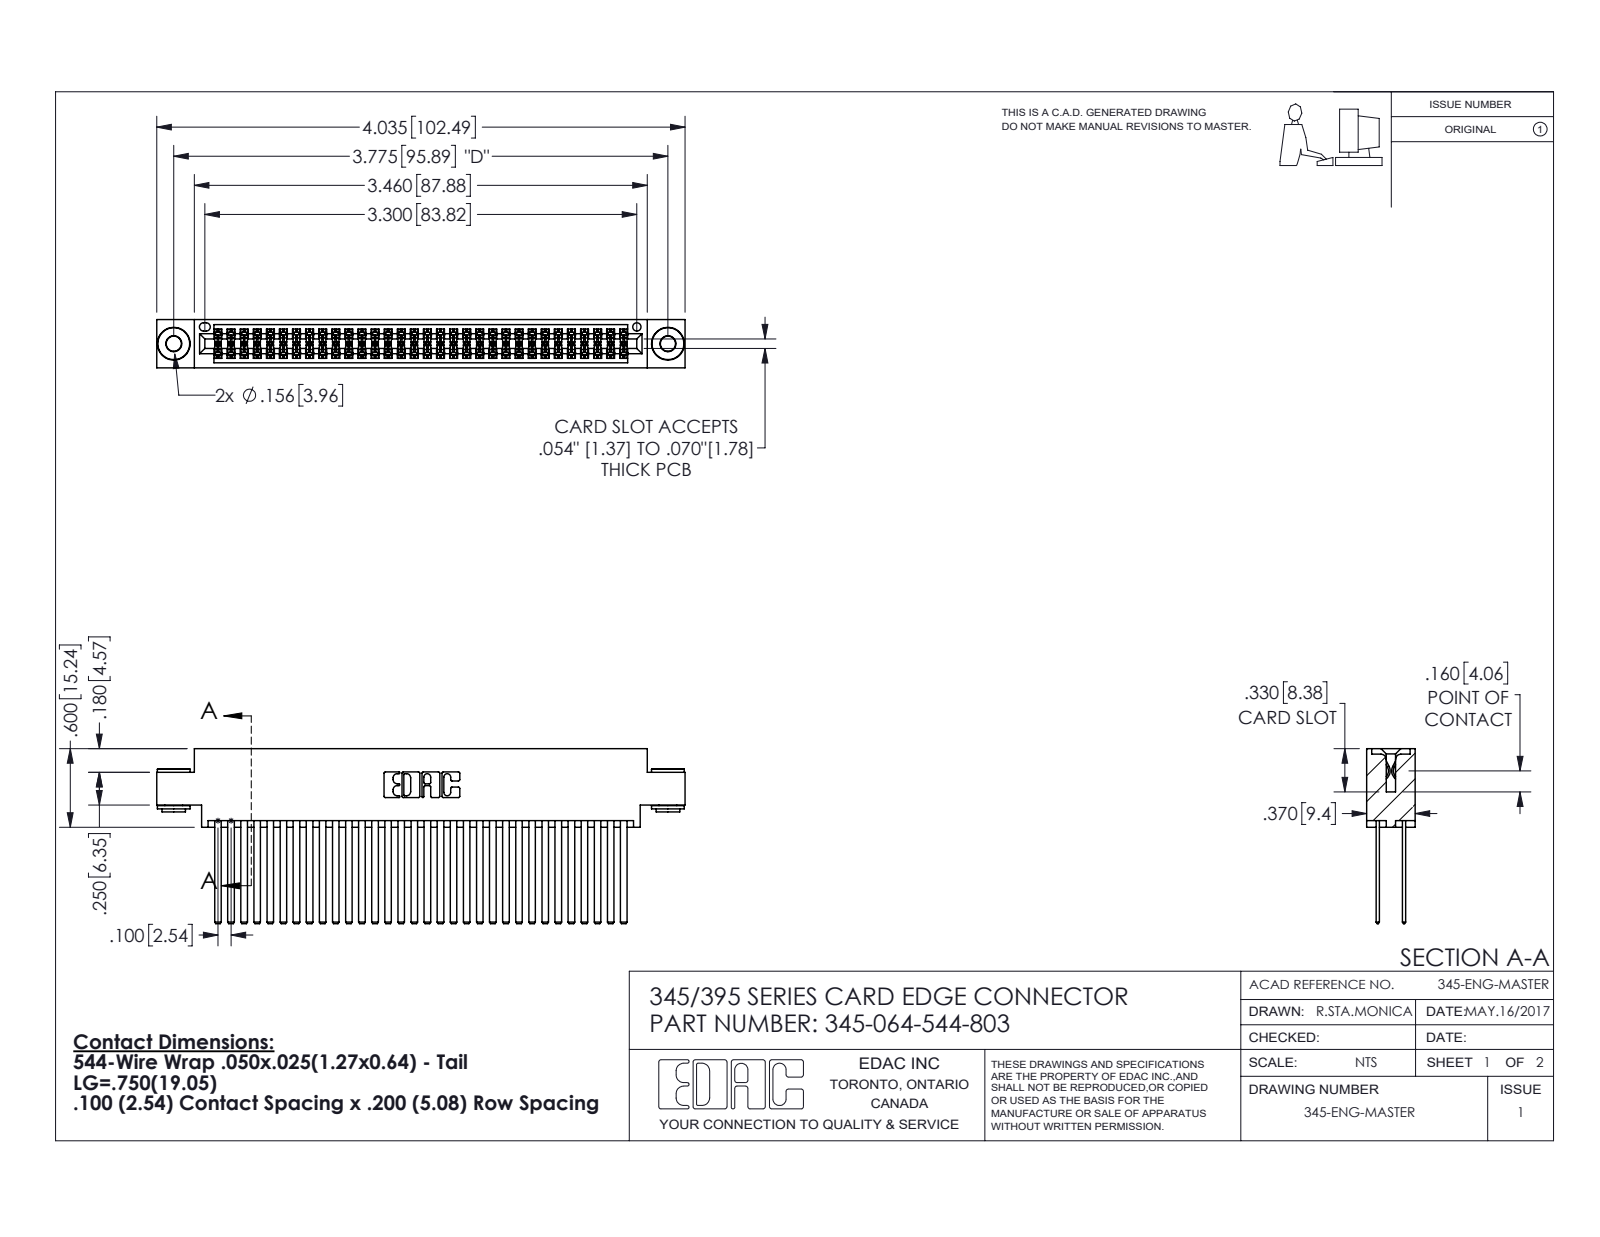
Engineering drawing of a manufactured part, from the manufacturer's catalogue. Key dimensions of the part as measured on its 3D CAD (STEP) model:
Part name (STEP PRODUCT): 345-064-544-803; 345-250-002_345-250-002-102; 345-292-001_345-293-144; 345 Part_0.170 Offset - 0.156 Dia-TH
STEP written by: SolidWorks 2016 (CONFIG_CONTROL_DESIGN)
Units: inches
Bodies: 67 solids, 2984 faces (1950 planar, 1026 cylindrical, 8 other)
Overall size (bounding box): 4.035 × 1.337 × 0.37
Volume: 0.651 in³ · Surface area: 28.75 in²
Round holes (diameter × count): ⌀0.116 ×2, ⌀0.156 ×2, ⌀0.064 ×1
Round bosses / shafts (diameter × count): ⌀0.25 ×2, ⌀0.18 ×2, ⌀0.136 ×2
Partial cylindrical surfaces — rounded edges, fillets, slot ends (radius × count): R0.006 ×96, R0.01 ×22, R0.007 ×6, R0.031 ×6, R0.026 ×3, R0.014 ×2, R0.019 ×2, R0.022 ×2
Main face-to-face distances: 0.2, 0.025, 0.072, 0.098, 0.272, 0.298, 0.225, 0.175, 0.37, 0.15
Hole centre spacings: 0.27, 3.54, 3.775
